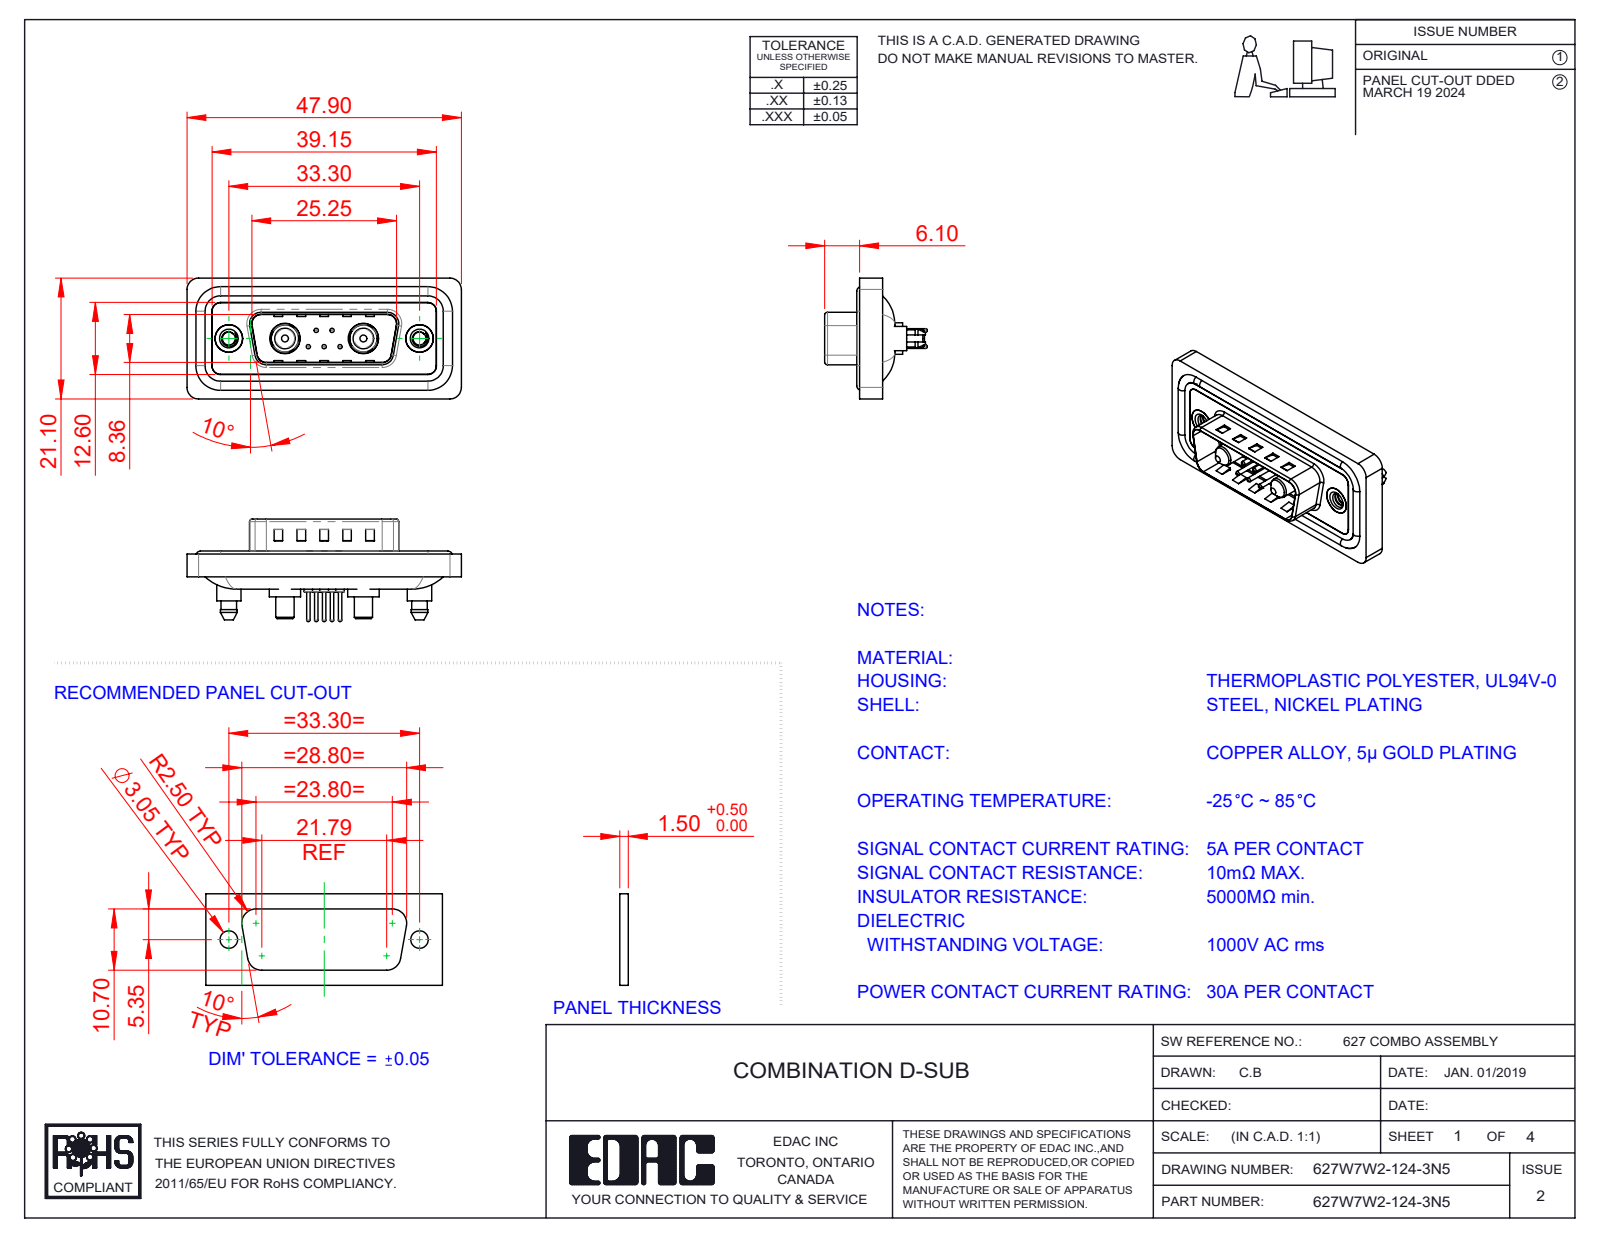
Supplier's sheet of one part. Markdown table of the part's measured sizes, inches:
| quantity | value |
| --- | --- |
| part name | 627Combo Threaded Boardlock_5; 627Combo Waterproof Housing_15 Contacts; Power Pin_30A S; 627Combo Shell Rear_15 Contacts (+5 more) |
| STEP written by | SolidWorks 2023 (CONFIG_CONTROL_DESIGN) |
| units | inches |
| bodies | 16 solids, 760 faces (248 planar, 324 cylindrical, 188 other) |
| overall size | 1.886 × 0.831 × 0.705 |
| volume | 0.346 in³ |
| surface area | 14.16 in² |
| round holes (diameter × count) | 0.03 × 5, 0.063 × 5, 0.079 × 5, 0.089 × 2, 0.157 × 2, 0.189 × 2, 0.191 × 2, 0.197 × 2, 0.209 × 2 |
| round bosses / shafts (diameter × count) | 0.059 × 5, 0.024 × 5, 0.063 × 4, 0.217 × 2, 0.213 × 2, 0.205 × 2, 0.193 × 2, 0.187 × 2 |
| partial cylindrical surfaces (radius × count) | 0.059 × 28, 0.079 × 20, 0.063 × 10, 0.02 × 8, 0.01 × 4, 0.024 × 4, 0.026 × 4, 0.035 × 4 |
| main face-to-face distances | 0.016, 0.043, 0.059, 0.063, 0.02, 0.122, 0.114, 0.028, 0.157, 0.032 |
| hole center spacings | 0.124, 0.109, 0.386, 0.925, 0.17, 0.17, 0.198, 0.198 |
